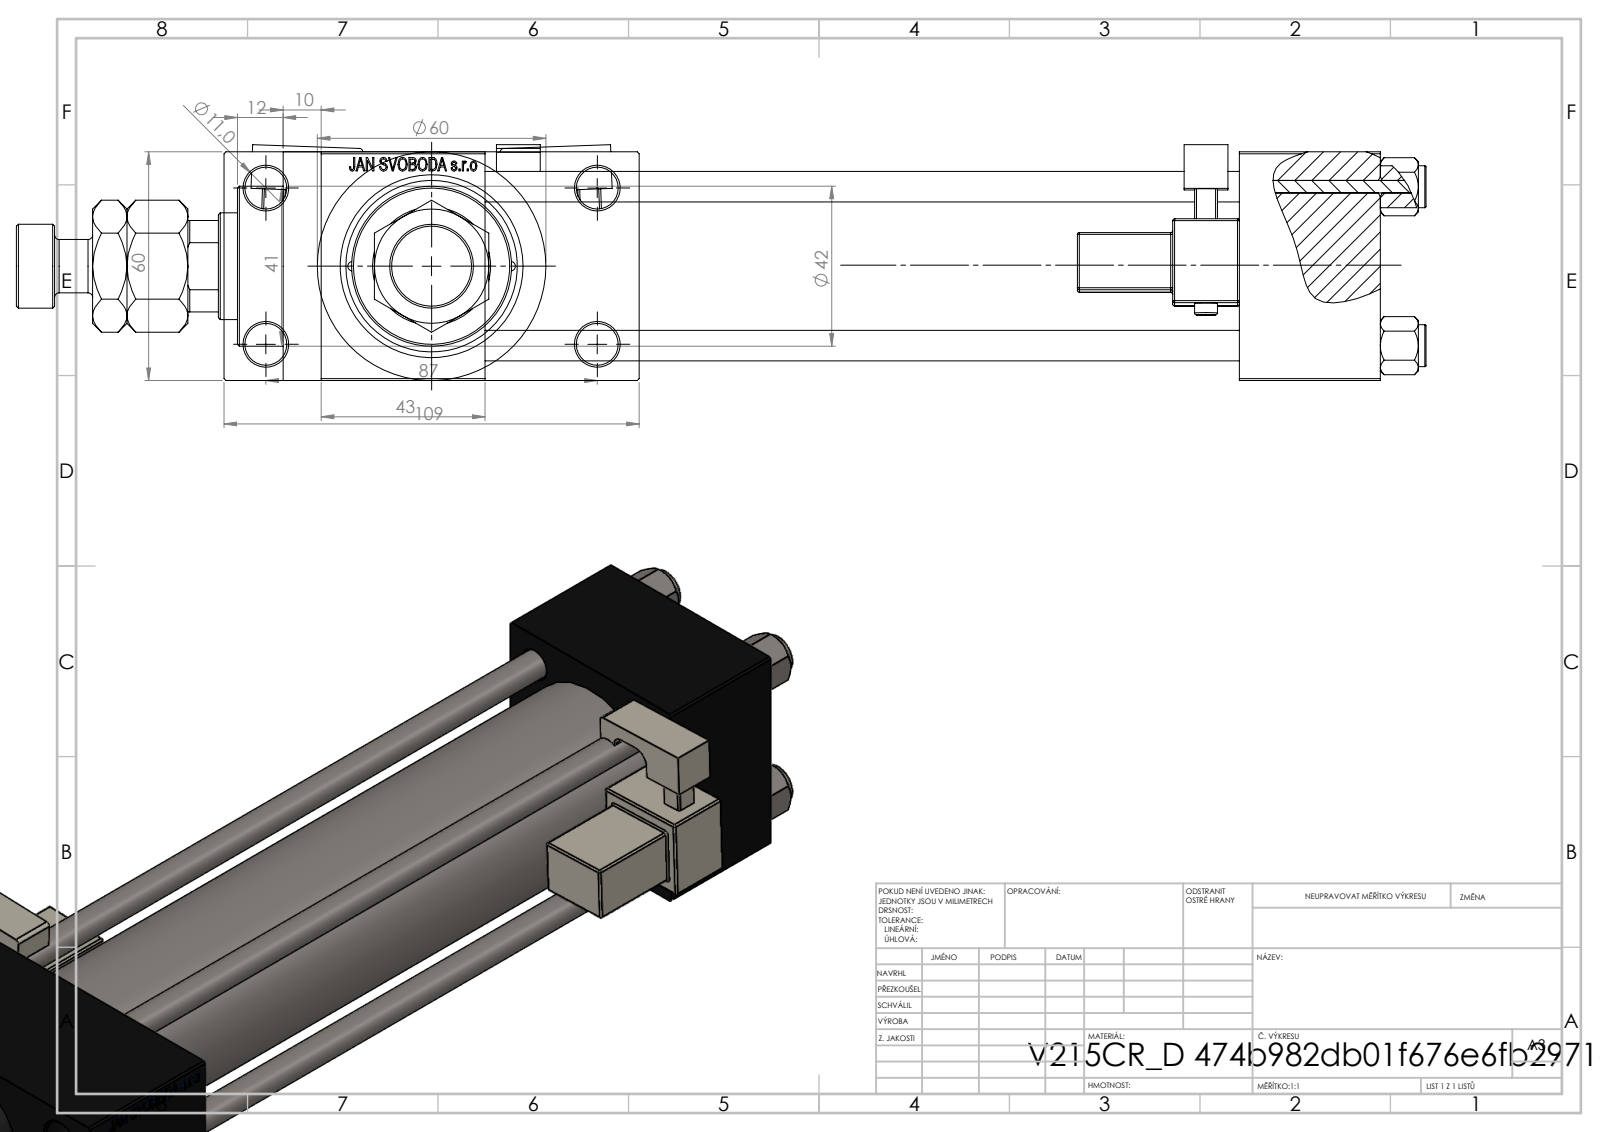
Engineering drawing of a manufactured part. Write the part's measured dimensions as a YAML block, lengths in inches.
part_name: "V215_VC_A; V215CR_MSU; V215CR_D_Body; MFA (+3 more)"
step_written_by: "SolidWorks 2019 (CONFIG_CONTROL_DESIGN)"
units: inches
bodies: {solids: 14, faces: 1320, planar: 576, cylindrical: 156, other: 588}
overall_size: [14.567, 4.291, 2.437]
volume: 46.7
surface_area: 327
round_holes:
  - {diameter: 0.315, count: 4}
  - {diameter: 0.433, count: 4}
  - {diameter: 0.098, count: 2}
  - {diameter: 0.276, count: 2}
  - {diameter: 0.656, count: 2}
  - {diameter: 0.945, count: 2}
  - {diameter: 0.728, count: 1}
  - {diameter: 1.102, count: 1}
  - {diameter: 1.22, count: 1}
  - {diameter: 1.575, count: 1}
  - {diameter: 1.772, count: 1}
round_bosses_or_shafts:
  - {diameter: 0.433, count: 4}
  - {diameter: 0.236, count: 2}
  - {diameter: 2.362, count: 1}
  - {diameter: 1.811, count: 1}
  - {diameter: 1.654, count: 1}
  - {diameter: 0.866, count: 1}
  - {diameter: 0.551, count: 1}
partial_cylinders:
  - {radius: 0.02, count: 48}
  - {radius: 0.039, count: 2}
  - {radius: 0.098, count: 2}
  - {radius: 0.157, count: 2}
  - {radius: 0.531, count: 1}
face_to_face_distances: [2.362, 7.795, 0.965, 3.327, 1.457, 9.252, 10.945, 9.488, 1.693, 4.291]
hole_center_spacings: [0.821, 0.892, 1.161, 1.206, 1.642, 1.832, 1.856, 1.893]
